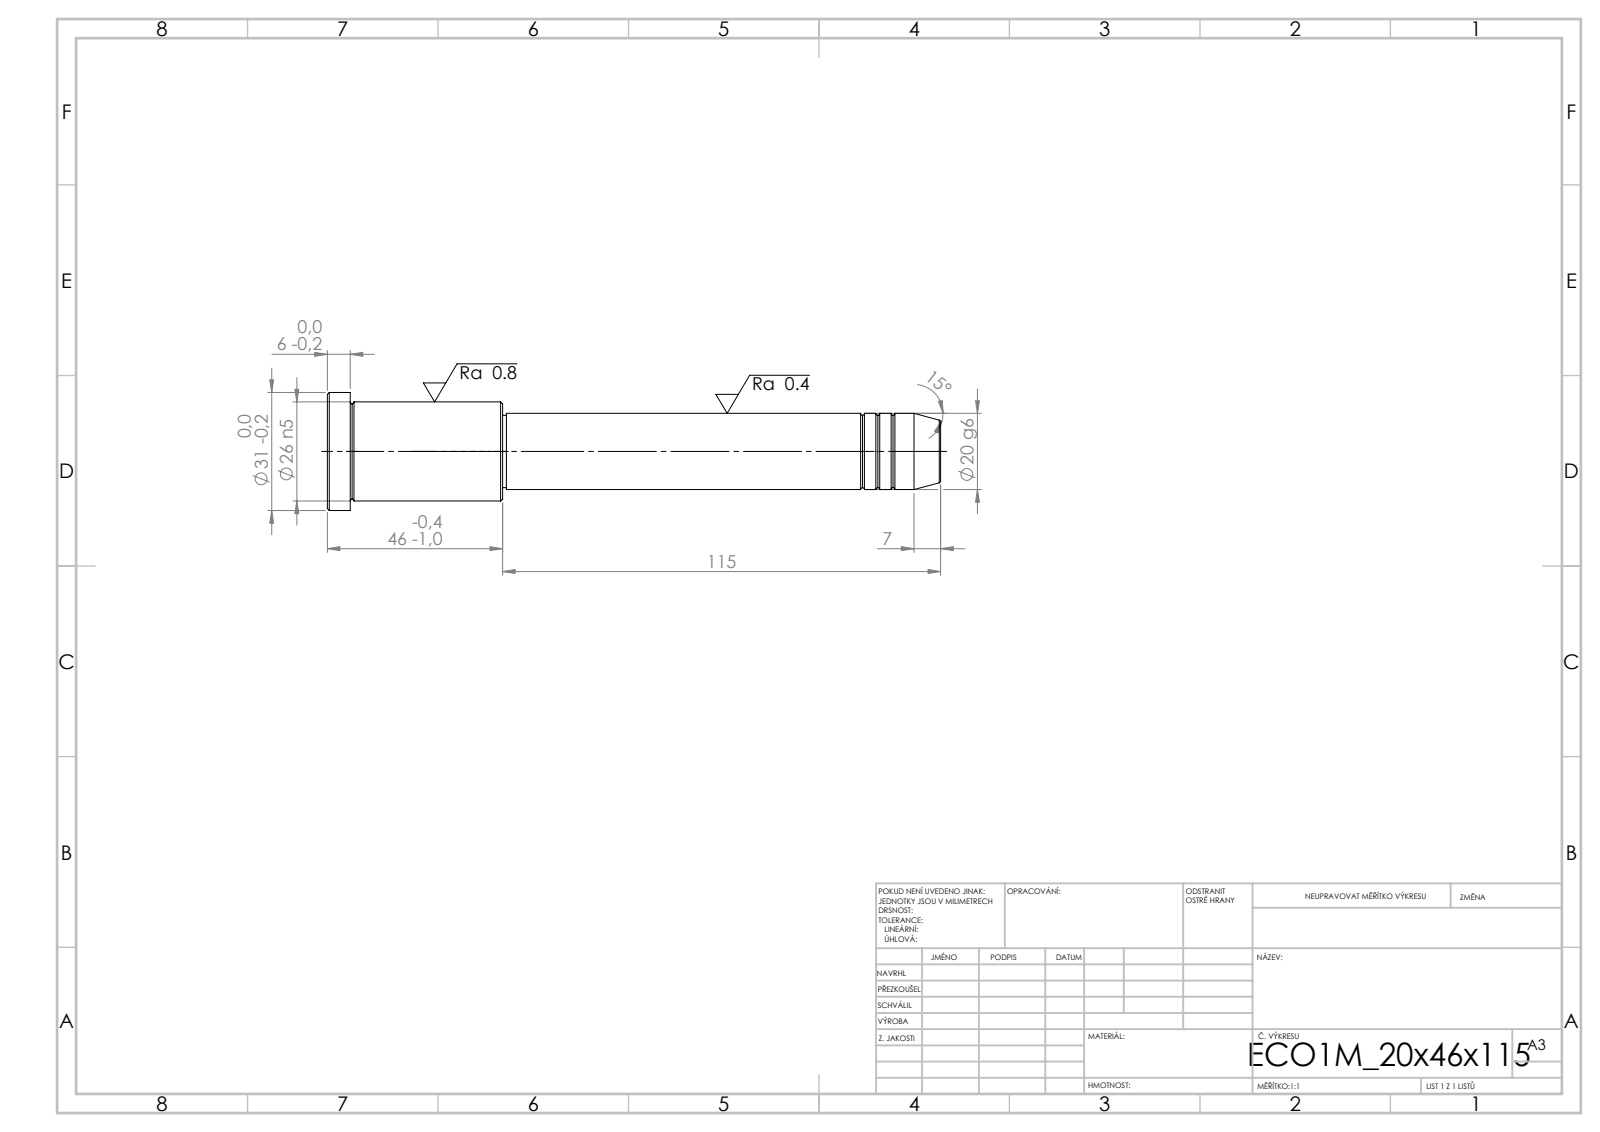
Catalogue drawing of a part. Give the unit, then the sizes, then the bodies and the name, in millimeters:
Units: millimetres
Overall size (bounding box): 161 × 31 × 31
Round bosses / shafts (diameter × count): ⌀31 ×1, ⌀26 ×1, ⌀20 ×1, ⌀19 ×1
Main face-to-face distances: 6, 40, 46, 115, 155, 161, 114, 1, 41, 47
Volume: 61 349 mm³ · Surface area: 12 594 mm²
Bodies: 1 solid, 43 faces (5 planar, 14 cylindrical, 24 other)
STEP written by: SolidWorks 2019 (CONFIG_CONTROL_DESIGN)
